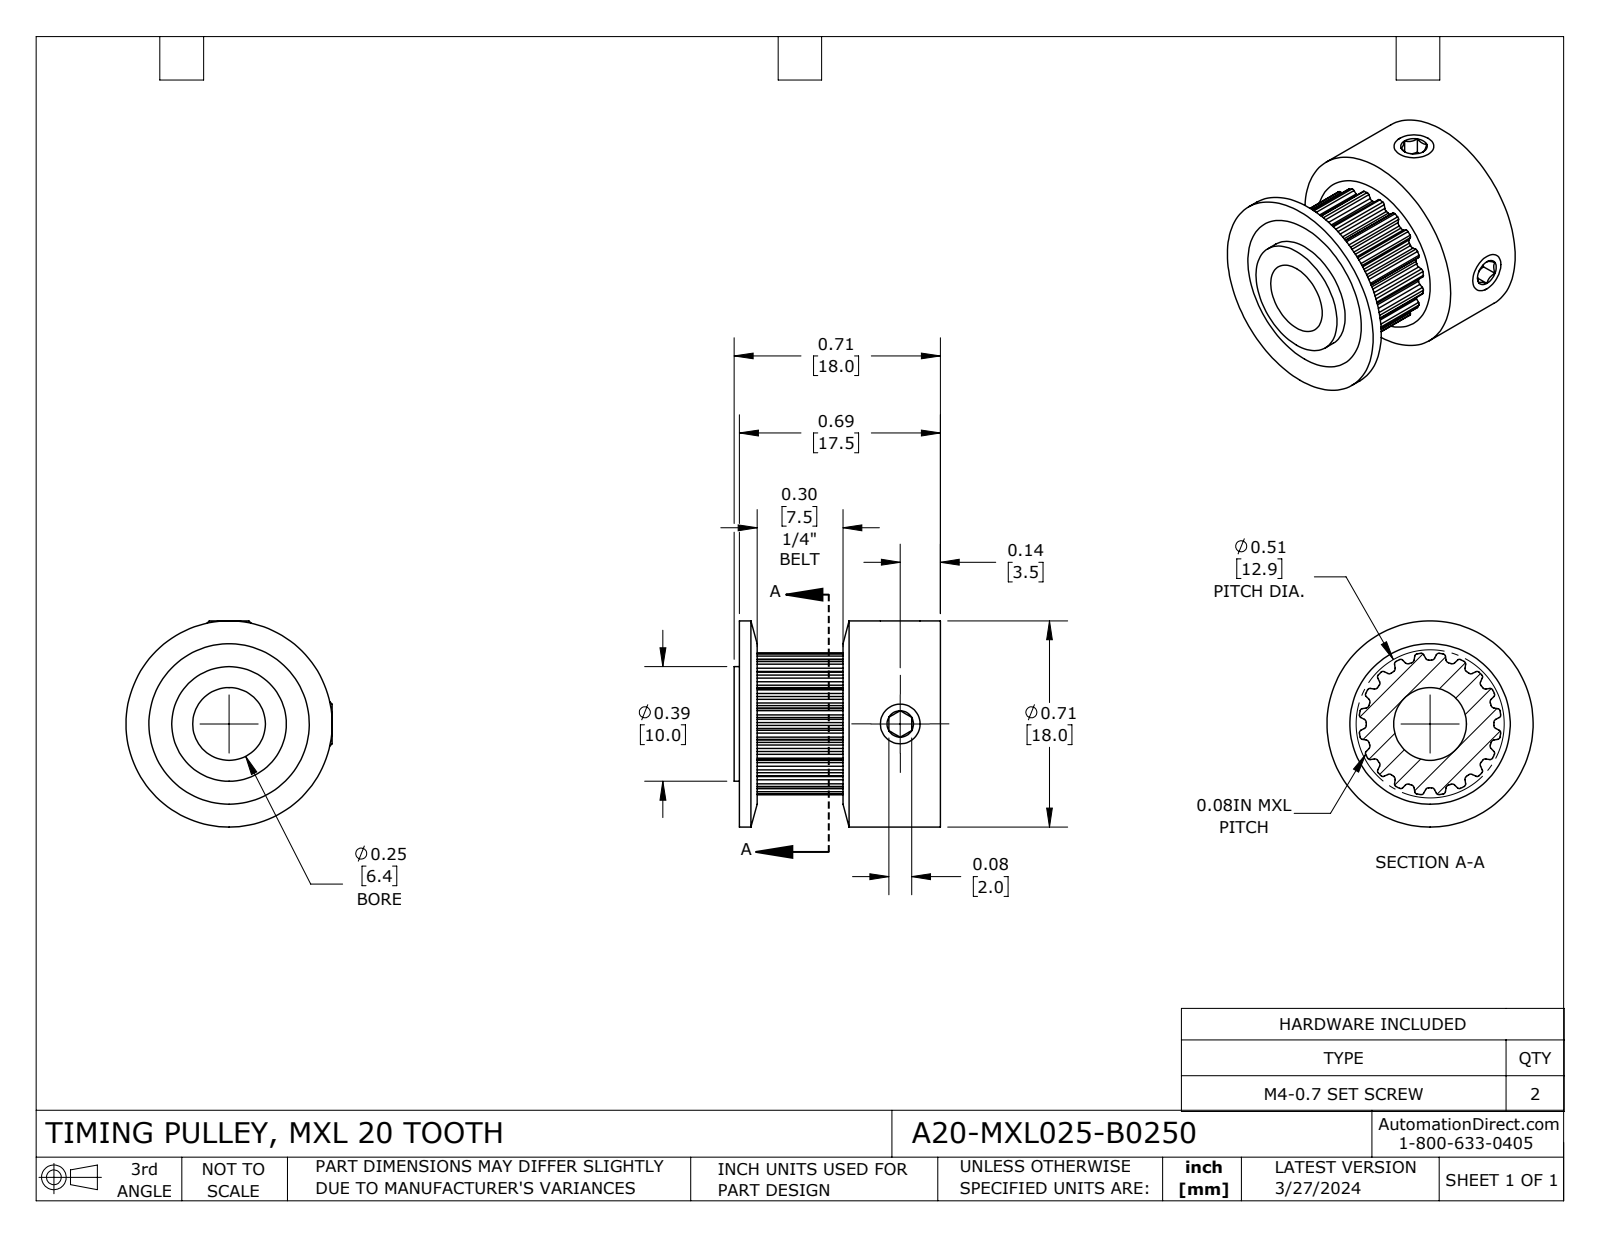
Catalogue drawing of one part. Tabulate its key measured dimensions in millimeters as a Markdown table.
| quantity | value |
| --- | --- |
| part name | A20-MXL025-B0250 |
| STEP written by | SolidWorks 2021 (CONFIG_CONTROL_DESIGN) |
| units | millimeters |
| bodies | 3 solids, 246 faces (61 planar, 153 cylindrical, 32 other) |
| overall size | 18 × 18 × 18 |
| volume | 2 674 mm³ |
| surface area | 2 243 mm² |
| round holes (diameter × count) | 3.3 × 2, 6.35 × 1 |
| round bosses / shafts (diameter × count) | 4 × 2, 18 × 1, 10 × 1 |
| partial cylindrical surfaces (radius × count) | 0.23 × 40, 0.3 × 40, 5.58 × 1, 6.21 × 1 |
| main face-to-face distances | 1, 8.5, 17, 2, 18, 16, 9.5, 7.5, 4.68, 4.7 |
